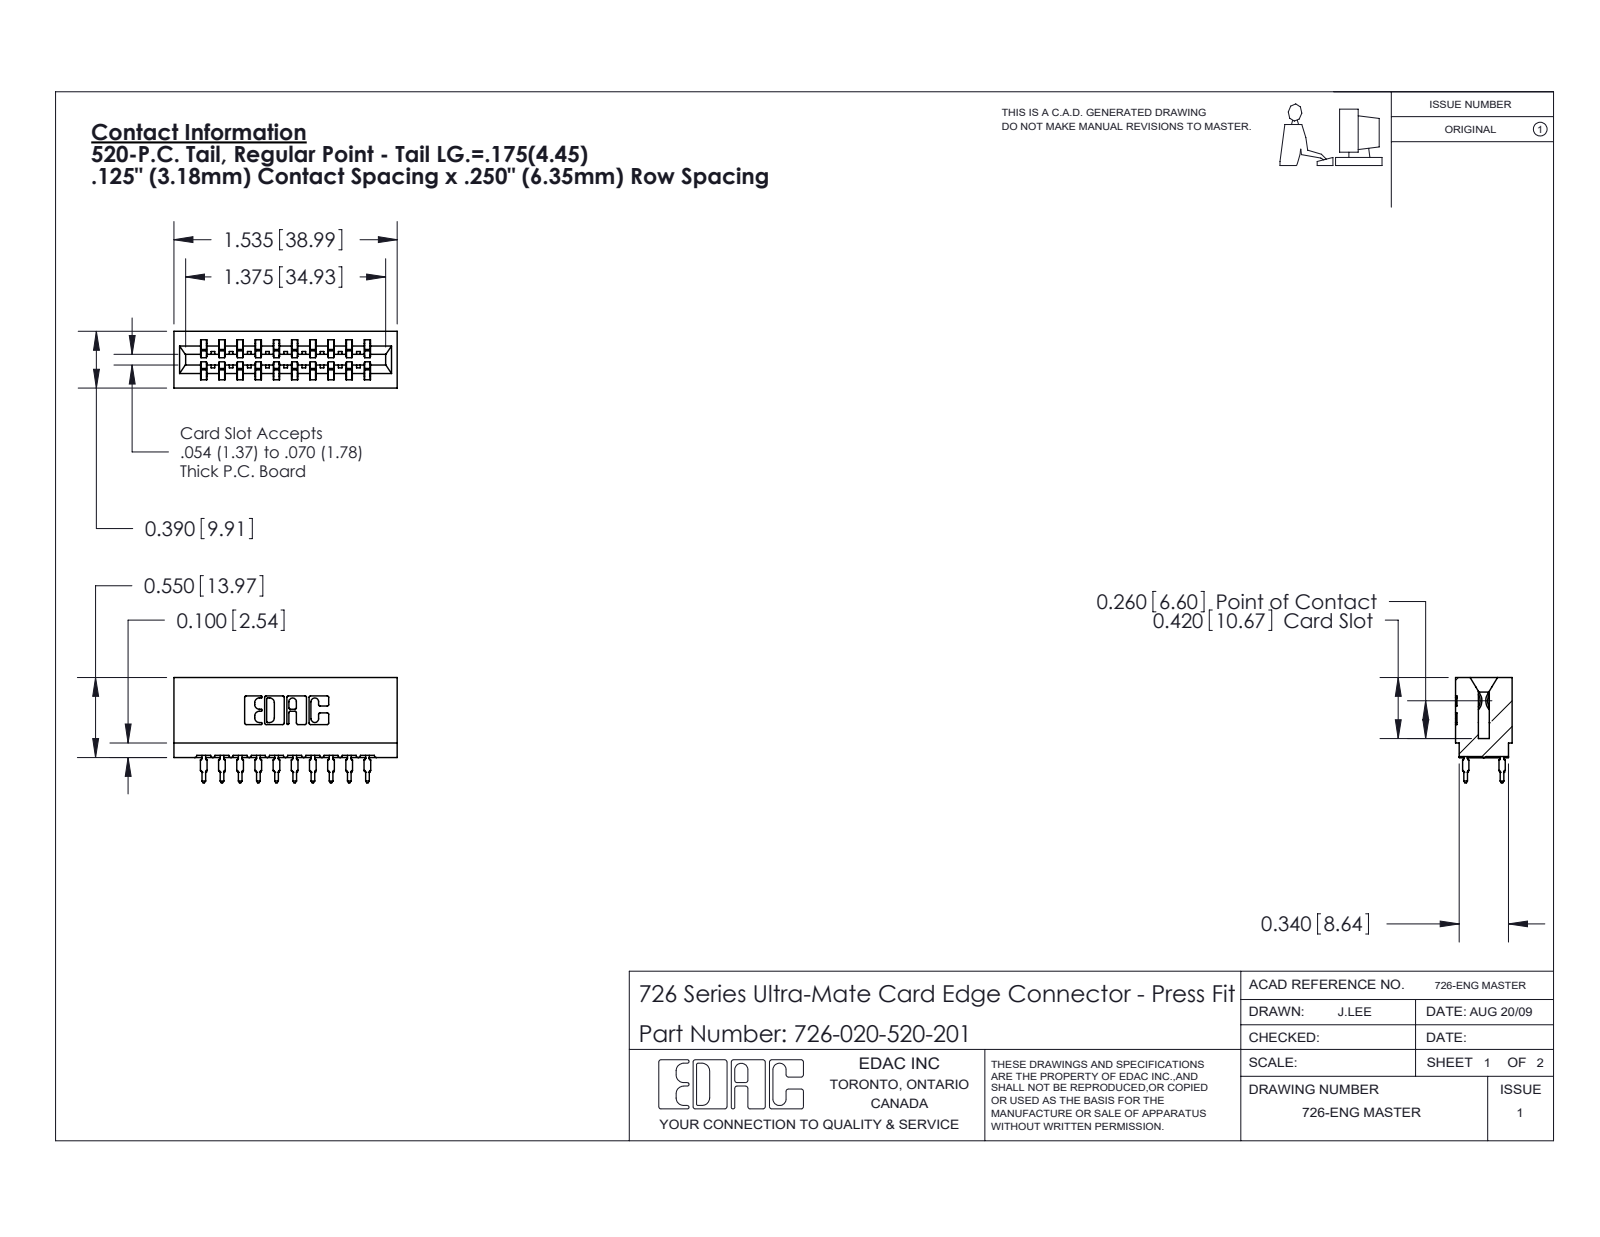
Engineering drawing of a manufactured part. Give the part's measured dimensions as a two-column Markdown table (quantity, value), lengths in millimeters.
| quantity | value |
| --- | --- |
| part name | 746-292-001_520; 726-020-520-201; 726 Part_.515 Slot Depth - 01 |
| STEP written by | SolidWorks 2020 (CONFIG_CONTROL_DESIGN) |
| units | millimeters |
| bodies | 21 solids, 1887 faces (975 planar, 392 cylindrical, 520 other) |
| overall size | 39 × 18.4 × 9.9 |
| volume | 3 740 mm³ |
| surface area | 5 579 mm² |
| partial cylindrical surfaces (radius × count) | 0.5 × 40, 0.3 × 22, 0.4 × 11, 0.1 × 8, 0.3 × 8, 0.2 × 6, 0.8 × 6, 0.7 × 3 |
| main face-to-face distances | 6.4, 1.4, 8.5, 3.2, 1.1, 19.1, 12.7, 9.9, 7.4, 9.5 |
